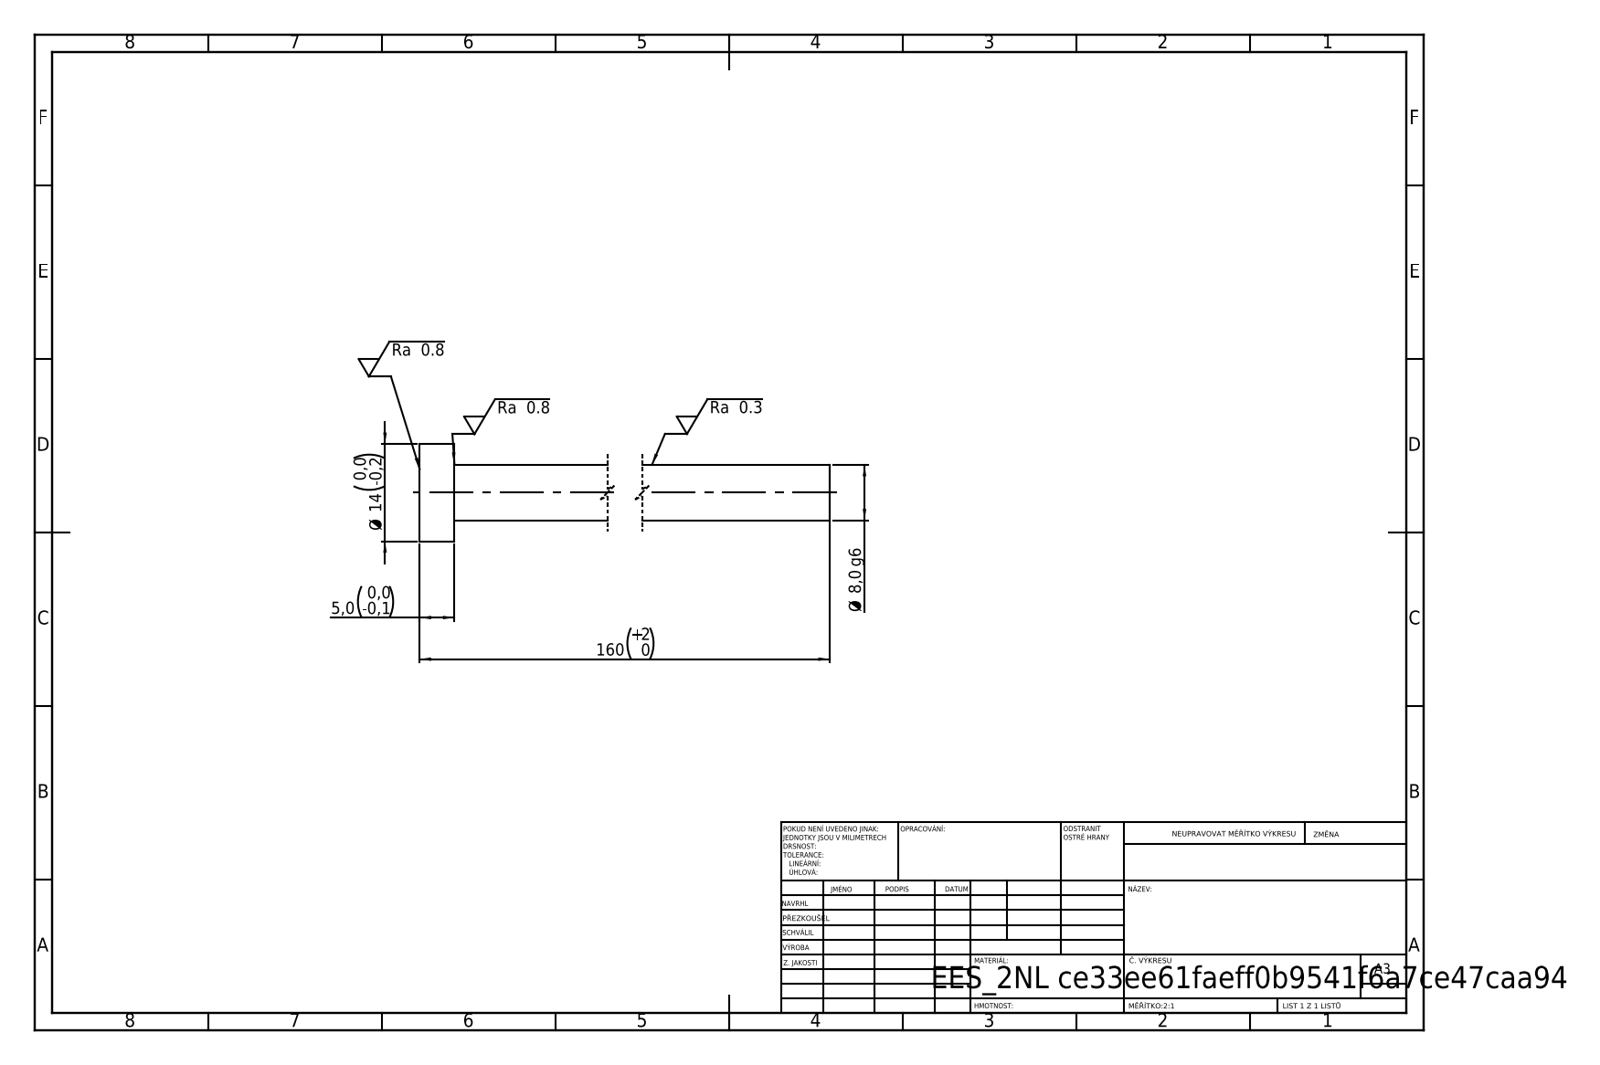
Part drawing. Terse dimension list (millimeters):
written by: SolidWorks 2019 (CONFIG_CONTROL_DESIGN)
unit: mm
bodies: 1 solid, 7 faces (3 planar, 4 cylindrical, 0 other)
size: 160 × 14 × 14
volume: 8 561 mm³; area: 4 423 mm²
bosses: 1× ⌀14, 1× ⌀8
face distances: 5, 160, 155
